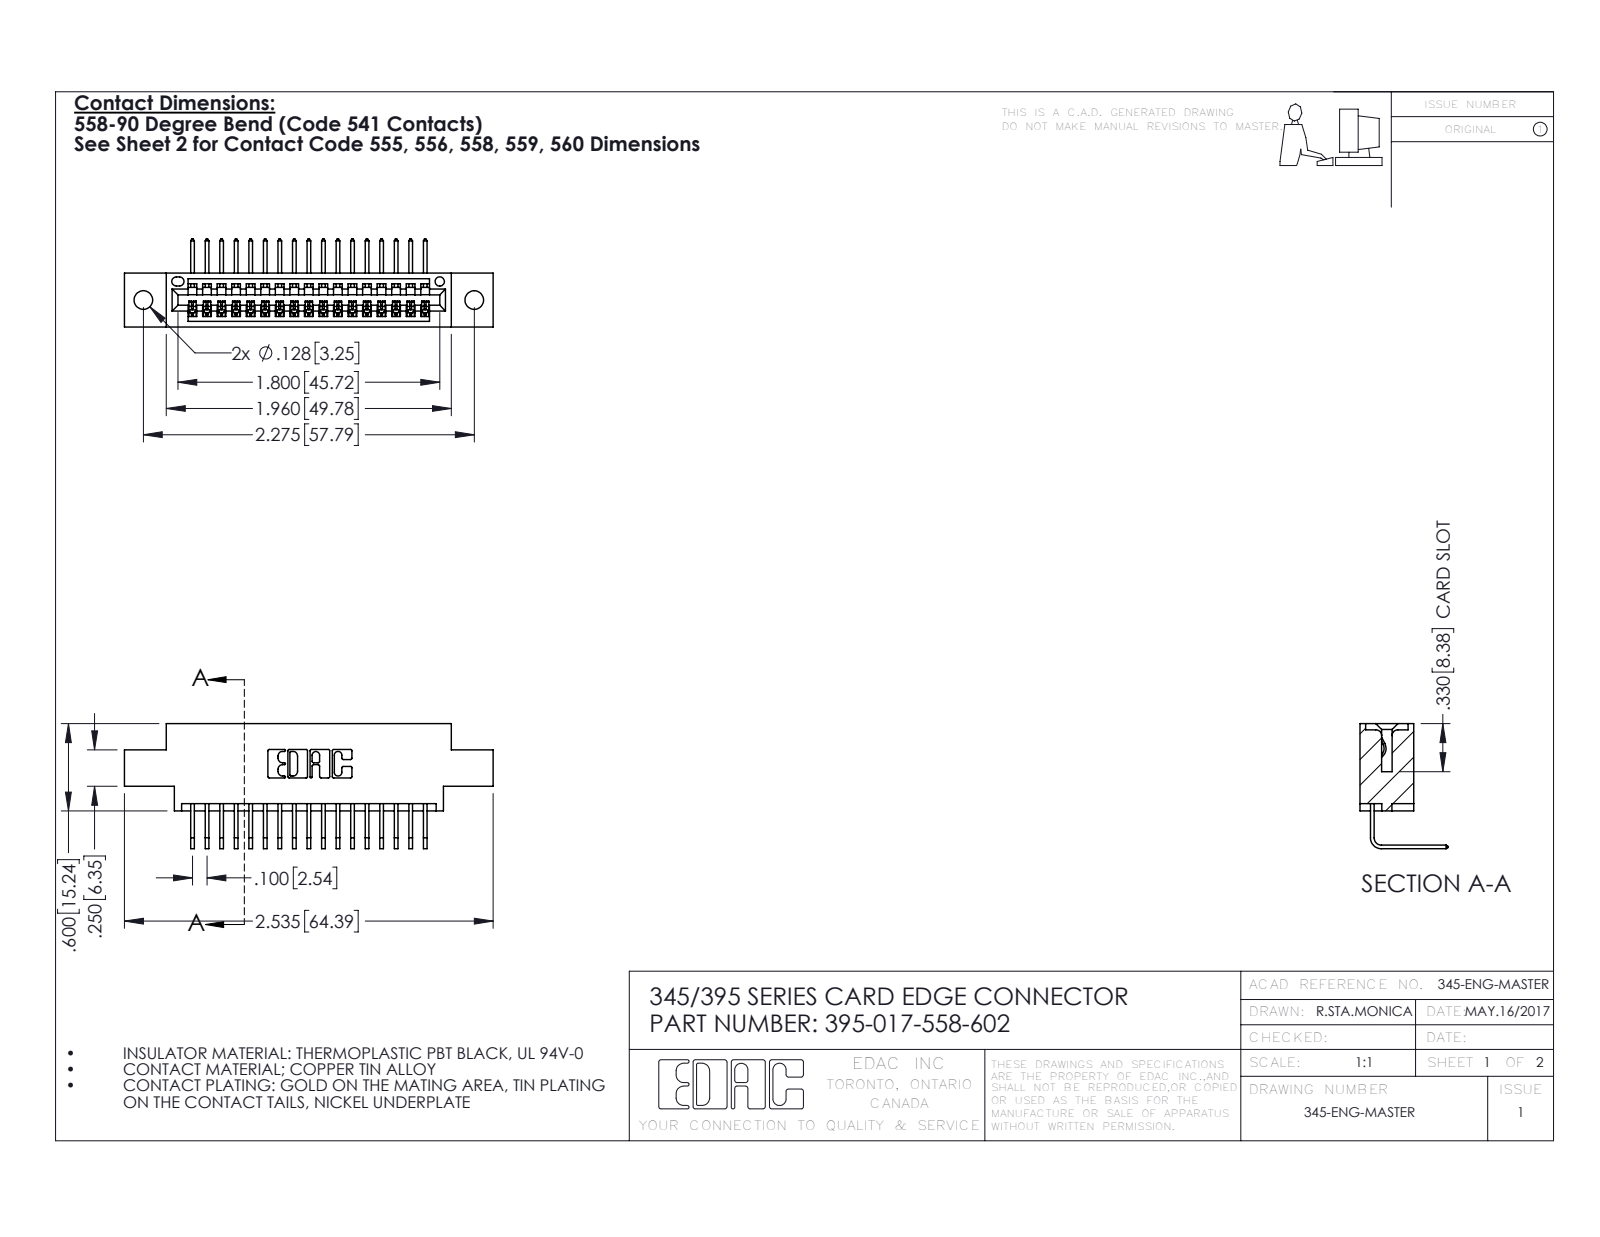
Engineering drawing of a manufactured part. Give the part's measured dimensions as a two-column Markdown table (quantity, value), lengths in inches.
| quantity | value |
| --- | --- |
| part name | 345-292-001_558 Tail - 2; 395-017-558-602; 345 Part_0.170 Offset - 0.128 Dia |
| STEP written by | SolidWorks 2016 (CONFIG_CONTROL_DESIGN) |
| units | inches |
| bodies | 18 solids, 1150 faces (798 planar, 352 cylindrical, 0 other) |
| overall size | 2.535 × 0.859 × 0.605 |
| volume | 0.355 in³ |
| surface area | 11.75 in² |
| round holes (diameter × count) | 0.128 × 2, 0.064 × 1 |
| partial cylindrical surfaces (radius × count) | 0.006 × 34, 0.01 × 22, 0.007 × 6, 0.031 × 6, 0.026 × 3, 0.031 × 2, 0.04 × 2, 0.014 × 1 |
| main face-to-face distances | 0.072, 0.298, 0.37, 0.2, 0.098, 0.272, 0.025, 0.225, 0.1, 0.15 |
| hole center spacings | 0.27, 2.041, 2.275 |
